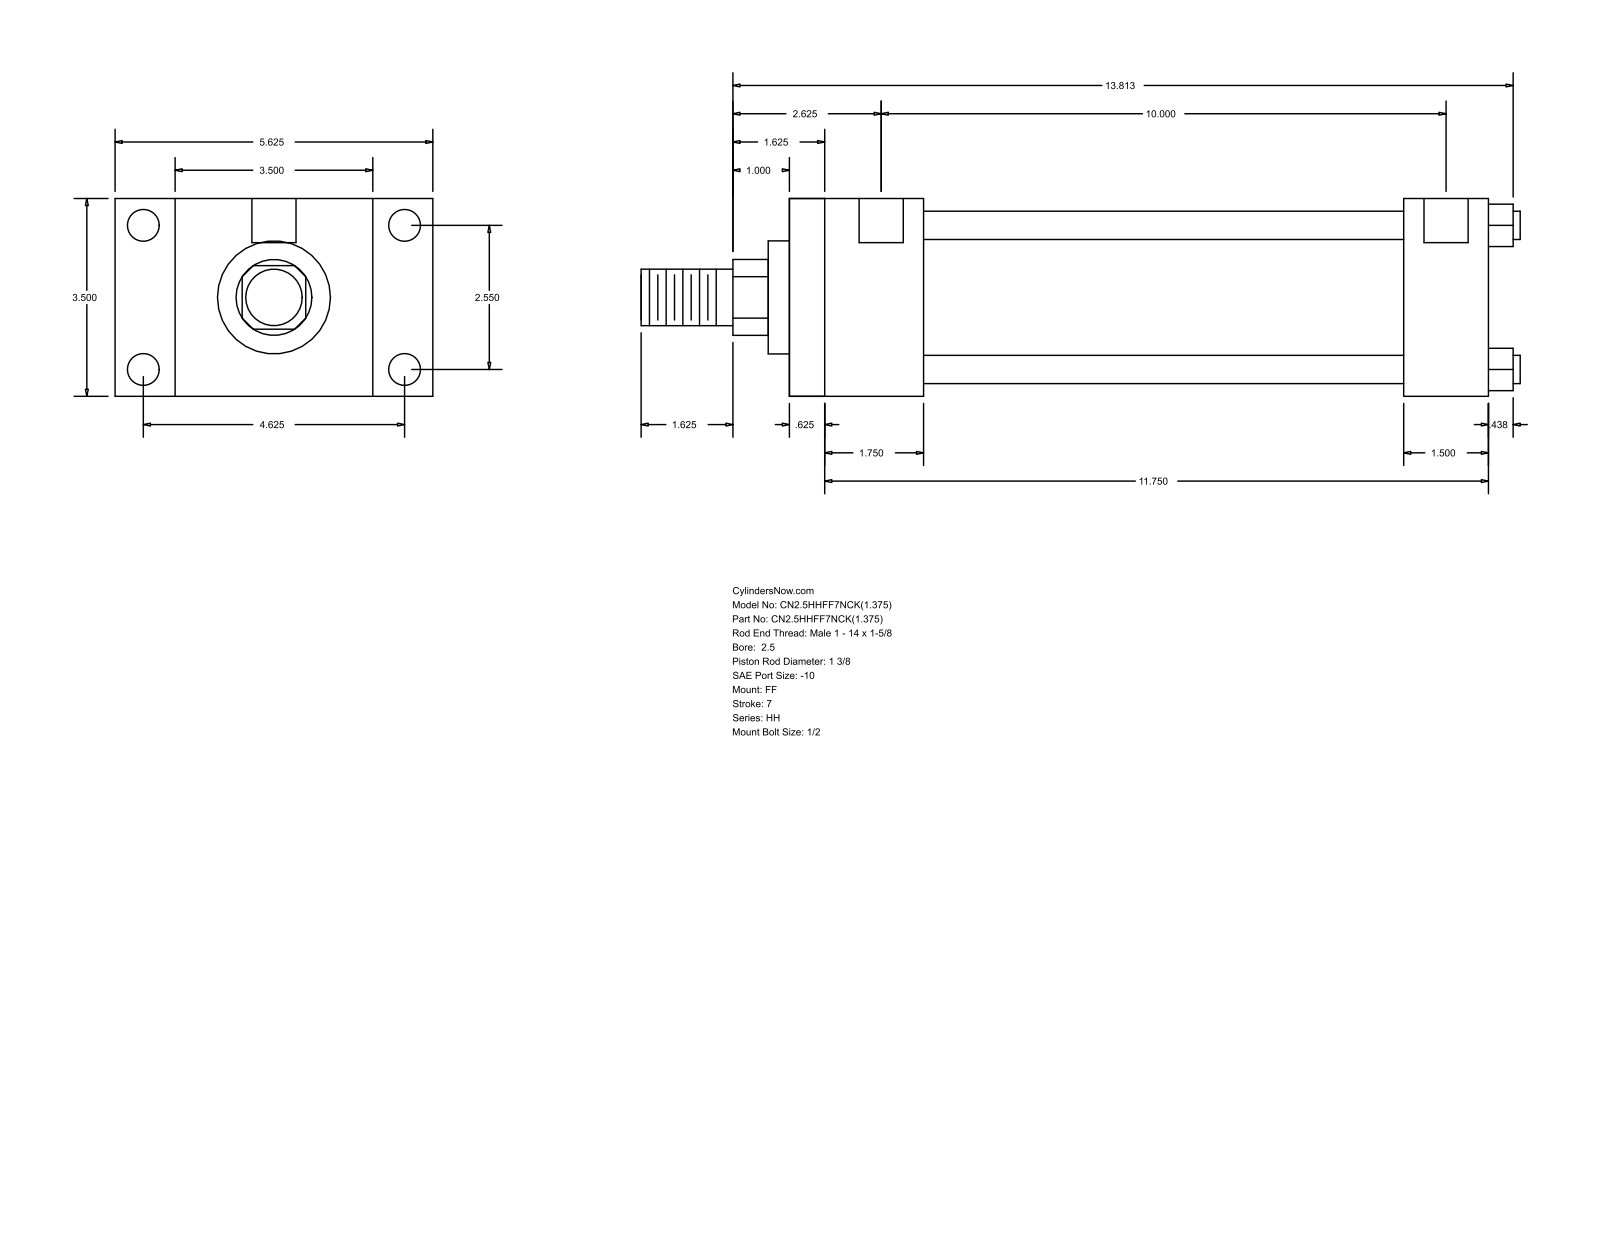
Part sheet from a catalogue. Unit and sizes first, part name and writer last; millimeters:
Units: millimetres
Overall size (bounding box): 395.29 × 142.88 × 88.9
Round holes (diameter × count): ⌀5.56 ×4, ⌀14.3 ×4, ⌀19.84 ×2
Round bosses / shafts (diameter × count): ⌀12.7 ×4, ⌀73.03 ×1, ⌀50.8 ×1, ⌀34.92 ×1, ⌀25.4 ×1
Partial cylindrical surfaces — rounded edges, fillets, slot ends (radius × count): R17.06 ×1
Main face-to-face distances: 88.9, 314.33, 15.87, 298.46, 60.32, 44.45, 254.01, 276.22, 260.35, 215.9
Hole centre spacings: 1.58, 64.76, 117.48, 134.15, 255.59, 257.17, 254.01
Bodies: 0 solids, 92 faces (64 planar, 28 cylindrical, 0 other)
Part name (STEP PRODUCT): HH_FF__0250_1.375
STEP written by: GSSL Pune (CONFIG_CONTROL_DESIGN)
